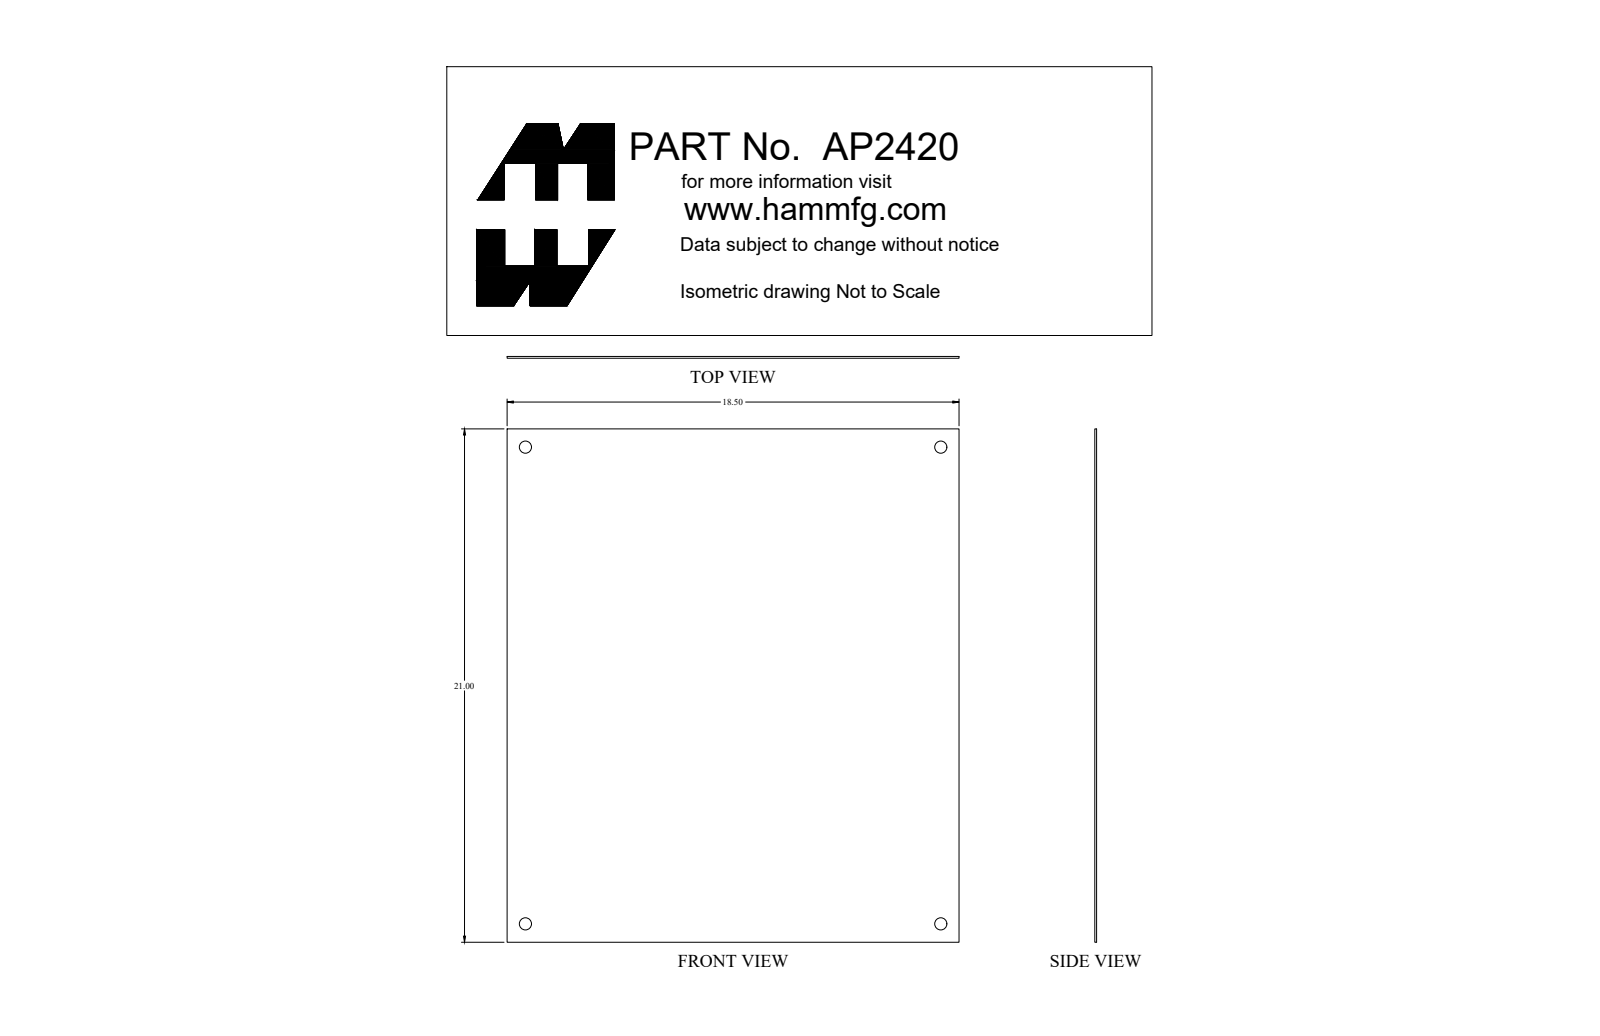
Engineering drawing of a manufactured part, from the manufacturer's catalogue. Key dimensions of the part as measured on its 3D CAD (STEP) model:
Part name (STEP PRODUCT): AP2420_Default
STEP written by: SolidWorks 2019 (CONFIG_CONTROL_DESIGN)
Units: inches
Bodies: 1 solid, 14 faces (6 planar, 8 cylindrical, 0 other)
Overall size (bounding box): 21 × 18.5 × 0.072
Volume: 27.92 in³ · Surface area: 781.6 in²
Round holes (diameter × count): ⌀0.5 ×4
Main face-to-face distances: 0.072, 18.5, 21
Hole centre spacings: 17, 19.5, 25.87
